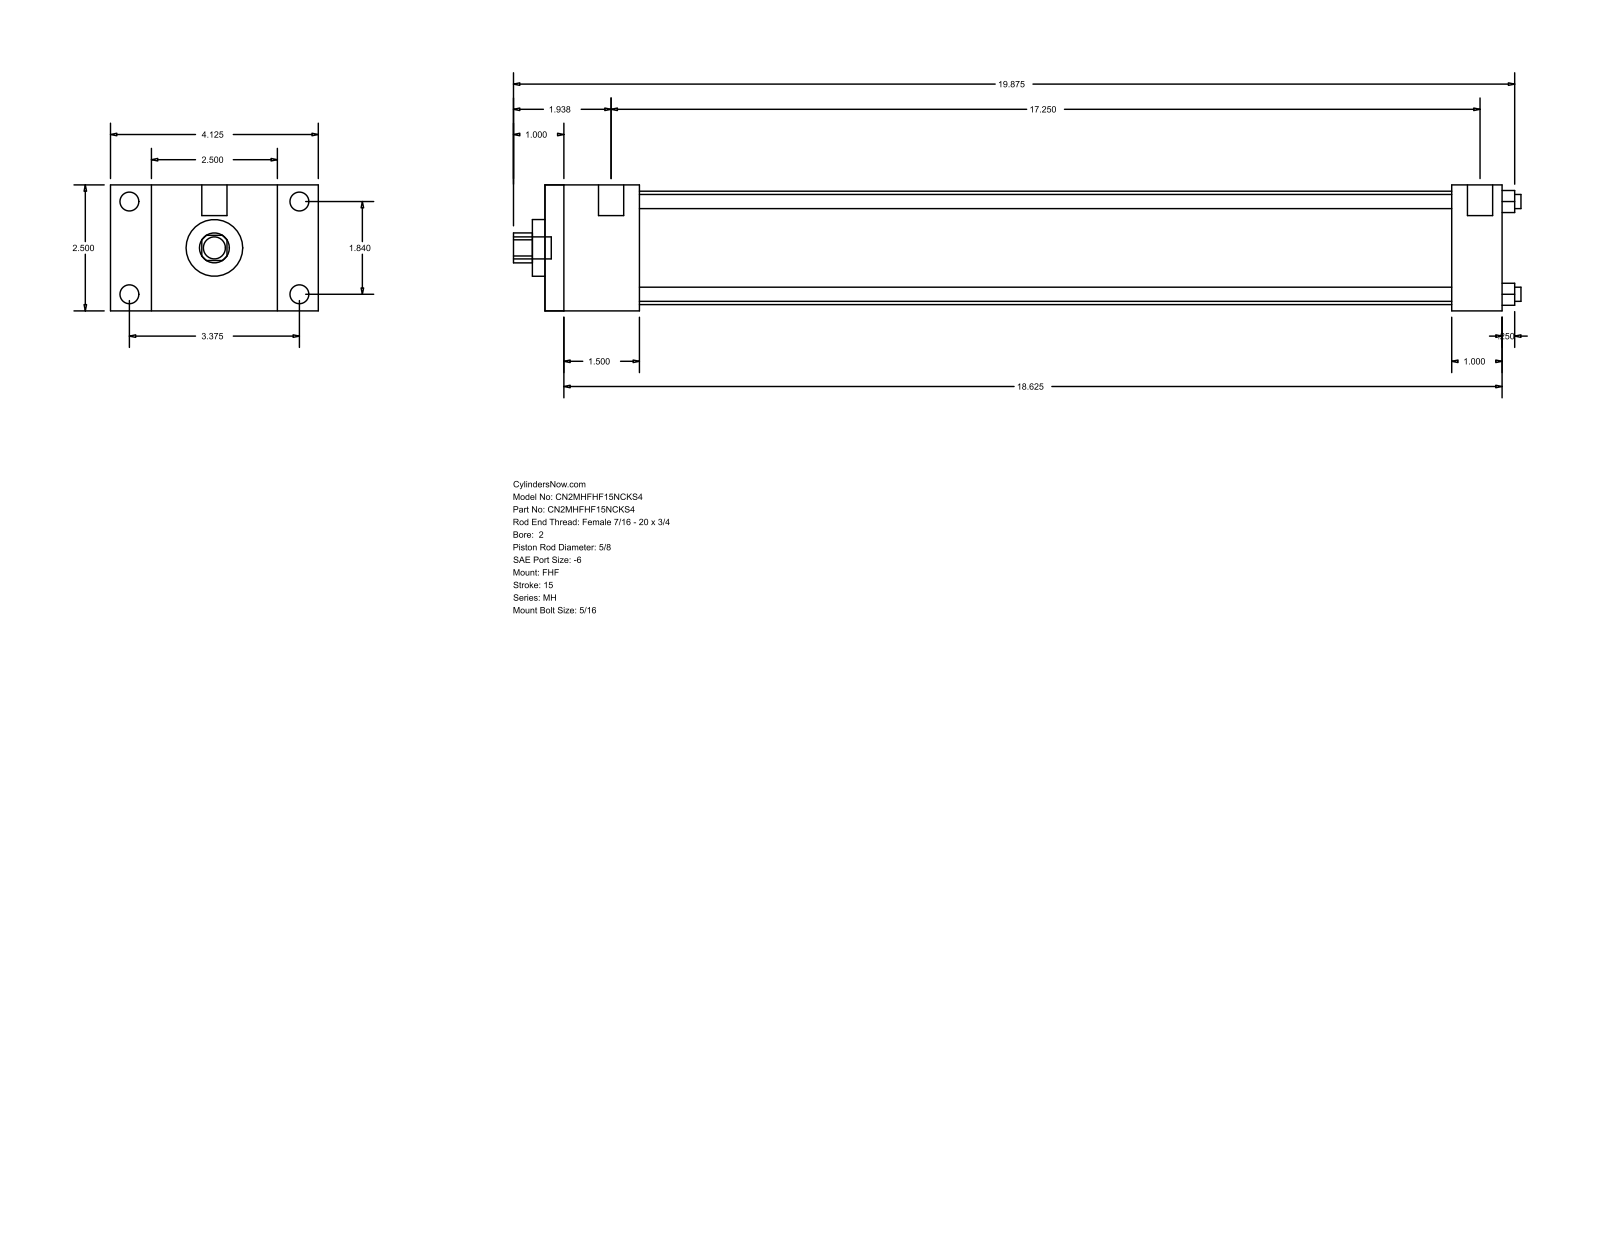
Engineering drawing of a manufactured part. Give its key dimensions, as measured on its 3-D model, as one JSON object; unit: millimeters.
{"part_name": "MH_FHF__0200_0.625", "step_written_by": "GSSL Pune (CONFIG_CONTROL_DESIGN)", "units": "millimeters", "bodies": {"solids": 0, "faces": 88, "planar": 60, "cylindrical": 28, "other": 0}, "overall_size": [508, 104.78, 63.5], "round_holes": [[7.14, 4], [15.88, 1], [28.57, 1], [57.15, 1]], "round_bosses_or_shafts": [[9.53, 4], [5.56, 4], [12.7, 2], [11.11, 1]], "partial_cylinders_radius": [[7.54, 1]], "face_to_face_distances": [63.5, 47.62, 482.6, 434.98, 20.64, 84.14, 104.78, 457.19, 409.57, 25.41], "hole_center_spacings": [33.05, 46.74, 66.1]}
